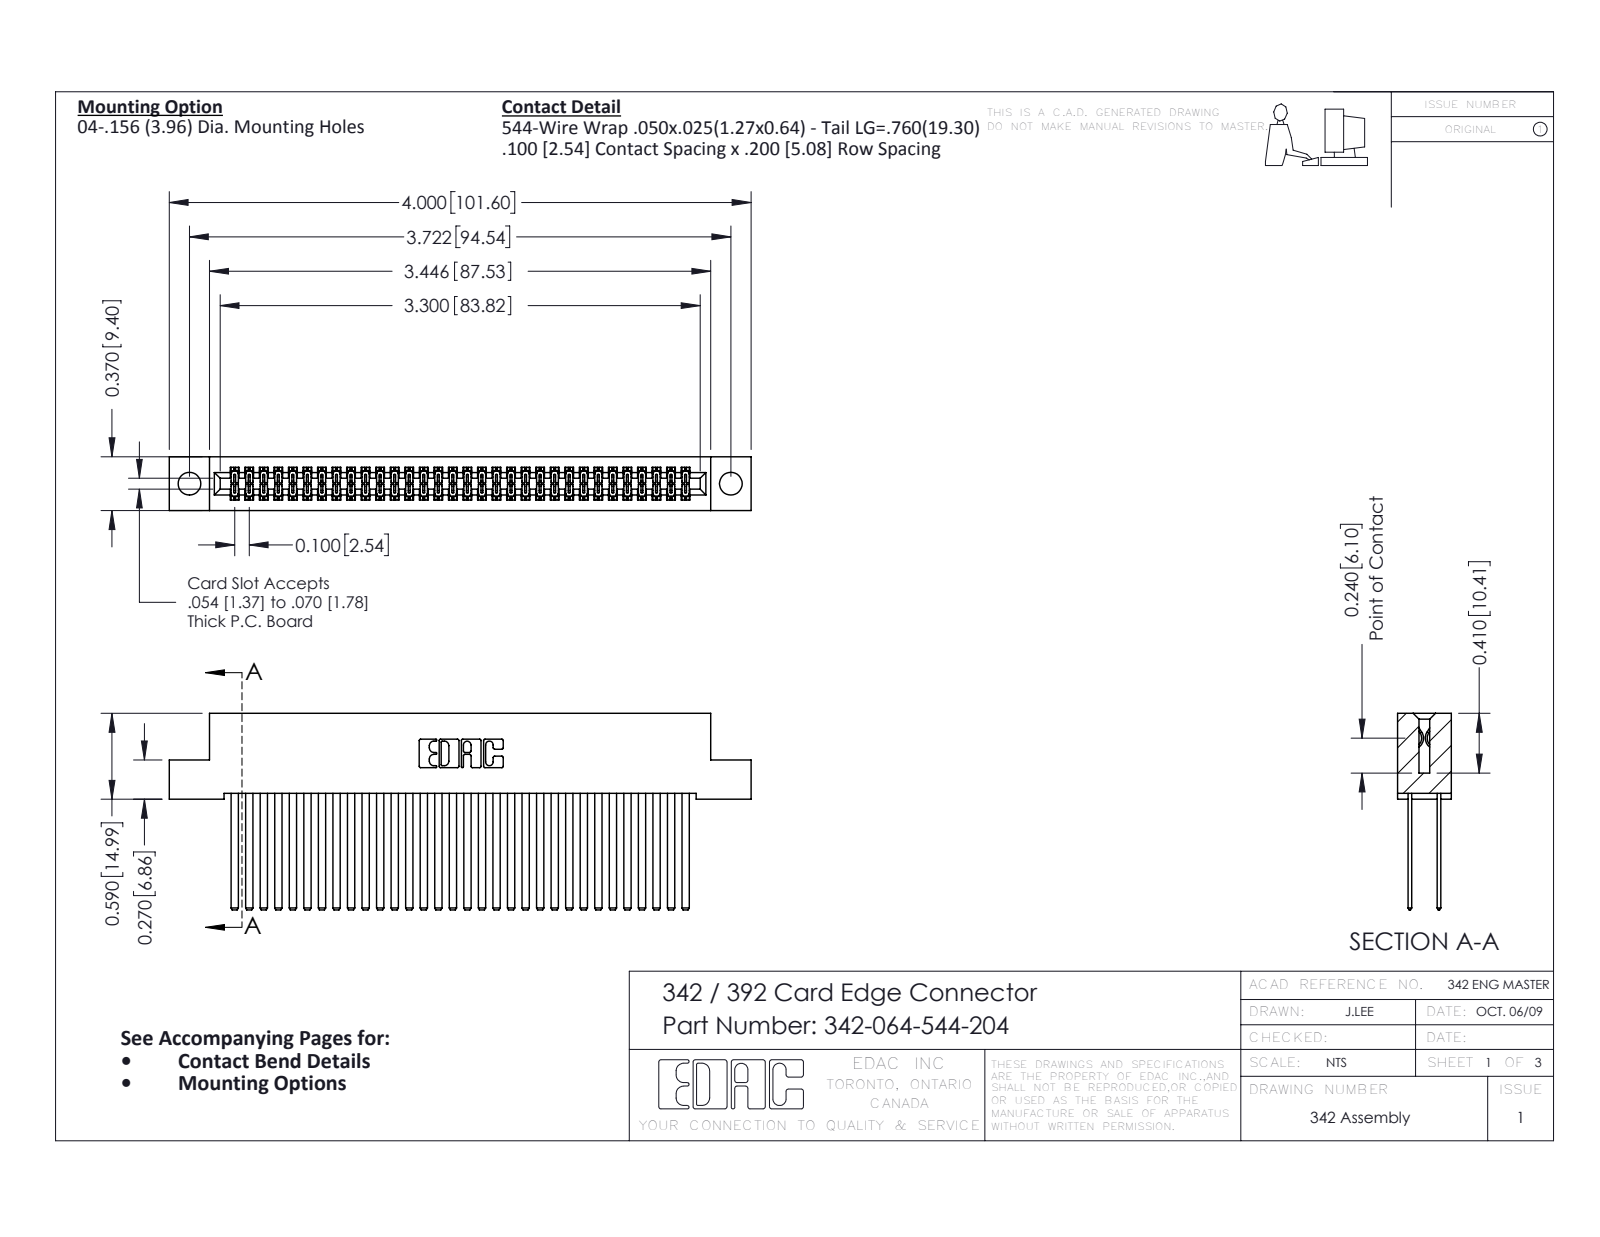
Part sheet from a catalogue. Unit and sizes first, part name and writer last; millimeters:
Units: millimetres
Overall size (bounding box): 101.6 × 34.3 × 9.4
Round holes (diameter × count): ⌀4 ×2
Partial cylindrical surfaces — rounded edges, fillets, slot ends (radius × count): R0.2 ×96, R0.3 ×22, R0.2 ×6, R0.8 ×6, R0.7 ×3, R0.4 ×2, R0.6 ×2, R0.6 ×2
Main face-to-face distances: 1.8, 7.6, 5.1, 2.5, 6.9, 0.6, 5.7, 9.4, 4.4, 1.9
Hole centre spacings: 94.5
Volume: 9 900 mm³ · Surface area: 18 160 mm²
Bodies: 65 solids, 3054 faces (2114 planar, 940 cylindrical, 0 other)
Part name (STEP PRODUCT): 342-064-544-204; 342 Part_.156 TH; 345-292-001_345-293-144
STEP written by: SolidWorks 2016 (CONFIG_CONTROL_DESIGN)
